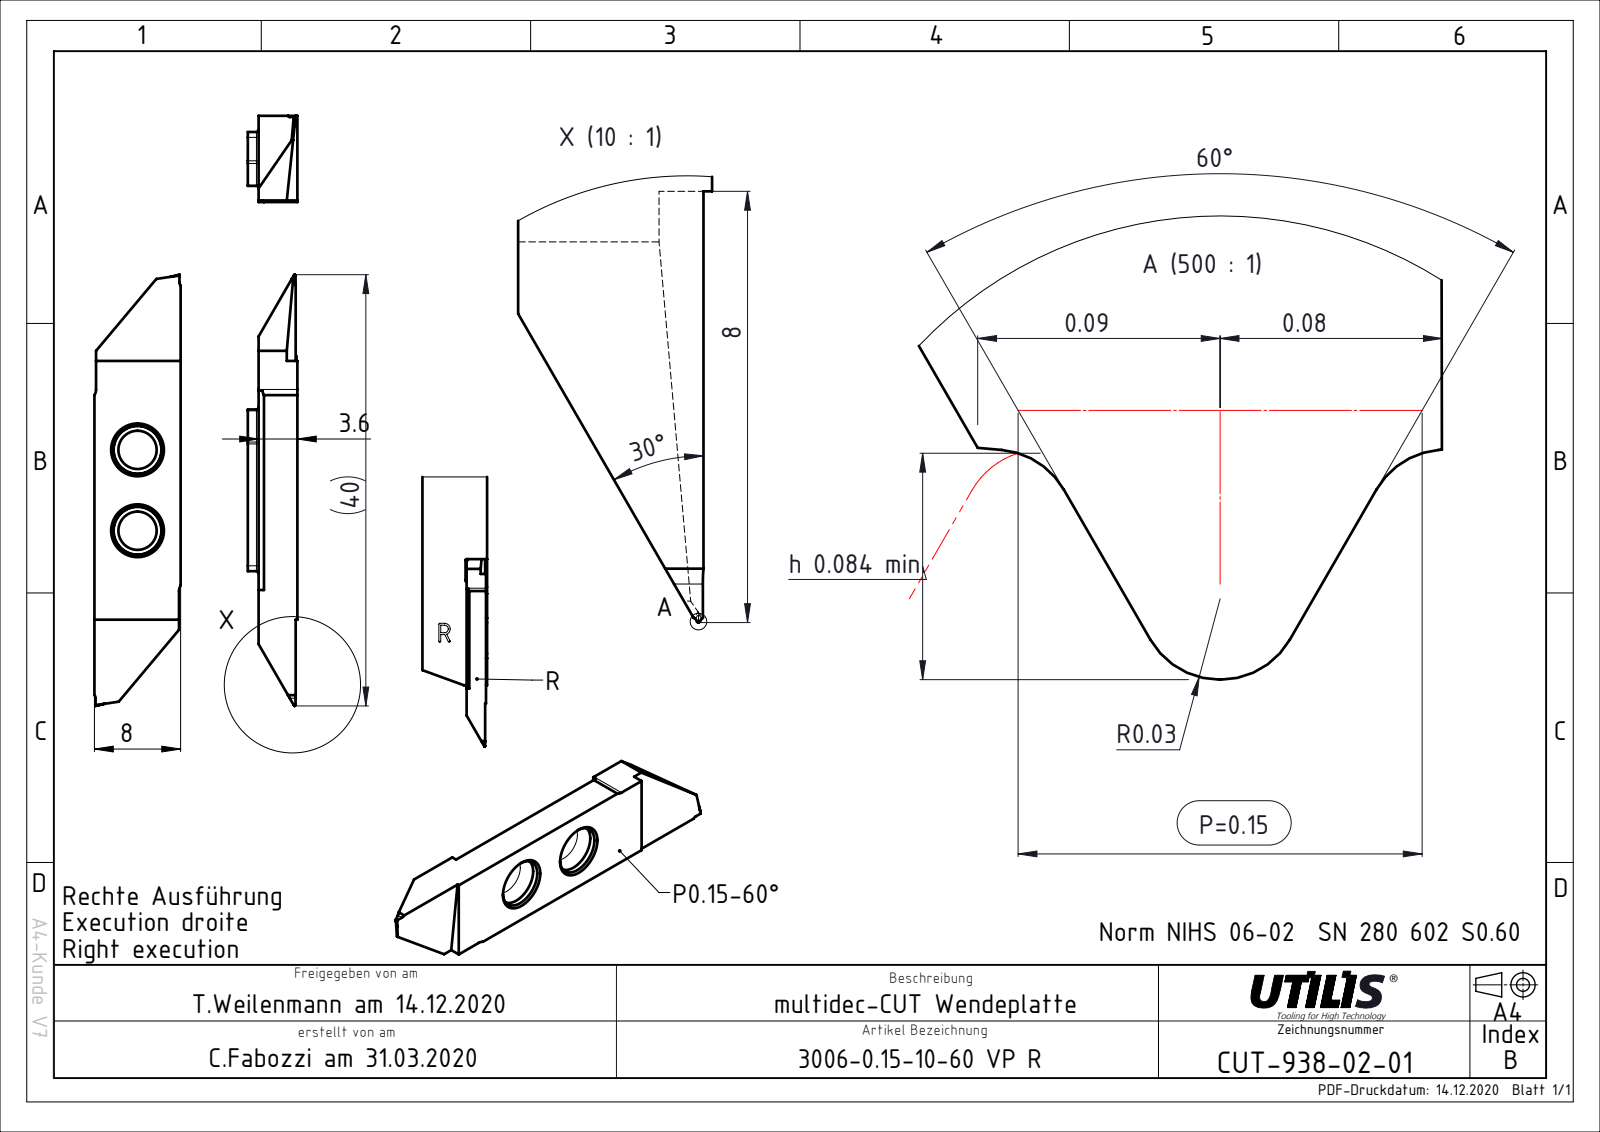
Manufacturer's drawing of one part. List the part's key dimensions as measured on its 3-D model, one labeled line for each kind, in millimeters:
Part name (STEP PRODUCT): CUT-938-02; ASME Y14.5
STEP written by: FormatWorks Professional (AP242_MANAGED_MODEL_BASED_3D_ENGINEERING_MIM_LF)
Units: millimetres
Bodies: 1 solid, 46 faces (30 planar, 16 cylindrical, 0 other)
Overall size (bounding box): 40 × 8 × 3.6
Volume: 807 mm³ · Surface area: 840 mm²
Round holes (diameter × count): ⌀3.55 ×2
Partial cylindrical surfaces — rounded edges, fillets, slot ends (radius × count): R1 ×2
Main face-to-face distances: 3.6, 8, 7.85, 22.54, 7.7, 24, 4, 4.15, 11.85, 12
Hole centre spacings: 7.5
